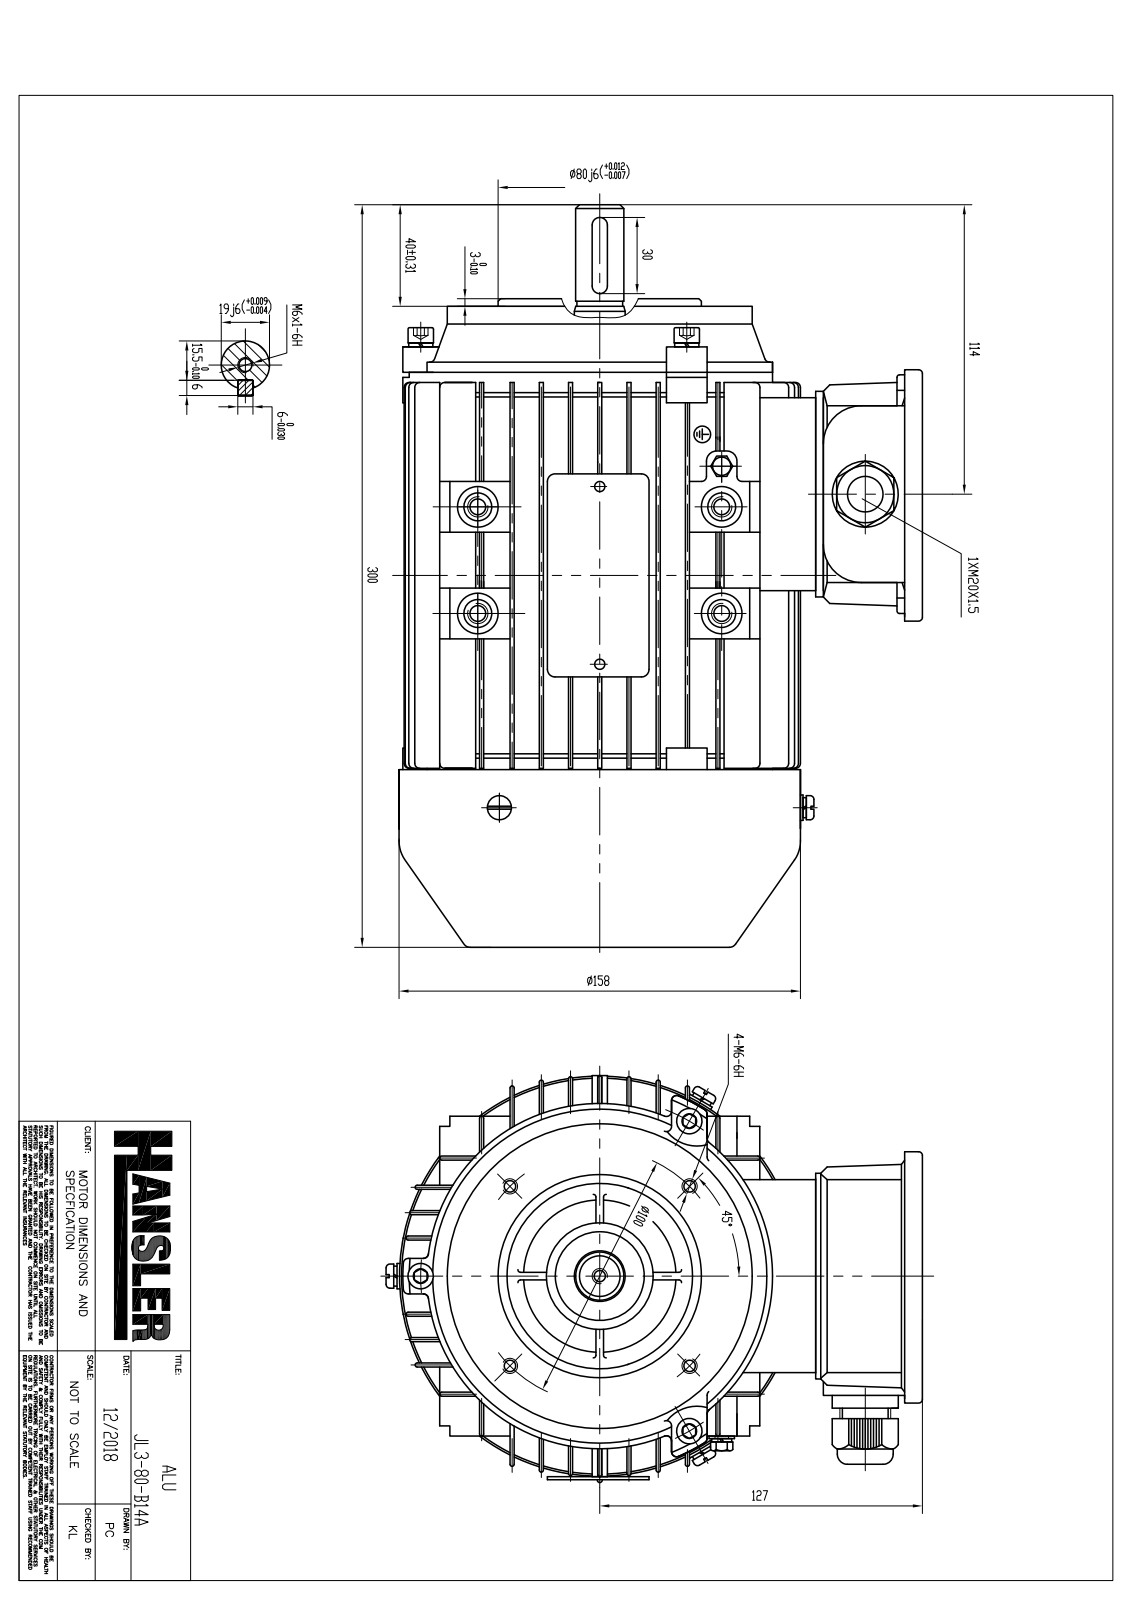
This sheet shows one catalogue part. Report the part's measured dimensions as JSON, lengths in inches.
{"part_name": "JL3-80-B14A", "step_written_by": "DATAKIT 2018 (c) (AP242_MANAGED_MODEL_BASED_3D_ENGINEERING_MIM_LF)", "units": "inches", "bodies": {"solids": 42, "faces": 2377, "planar": 1085, "cylindrical": 660, "other": 632}, "overall_size": [11.378, 11.034, 9.172], "volume_in3": 66.76, "surface_area_in2": 979.9, "round_holes": [[0.157, 13], [0.63, 10], [0.26, 8], [0.236, 5], [0.207, 4], [0.209, 4], [0.228, 4], [0.252, 3], [0.276, 3], [0.079, 2], [0.378, 2], [0.451, 2]], "round_bosses_or_shafts": [[0.433, 8], [0.472, 4], [0.394, 4], [0.309, 4], [0.276, 4], [0.197, 4], [0.176, 4], [0.157, 4]], "partial_cylinders_radius": [[0.039, 54], [0.079, 46], [0.118, 31], [0.013, 24], [0.012, 16], [0.015, 12], [0.078, 12], [0.197, 12]], "face_to_face_distances": [0.063, 0.453, 0.906, 1.358, 0.416, 1.811, 0.39, 0.516, 0.832, 0.843], "hole_center_spacings": [0.557, 1.654, 2.126, 3.425, 3.78, 4.126, 1.916, 2.776]}
